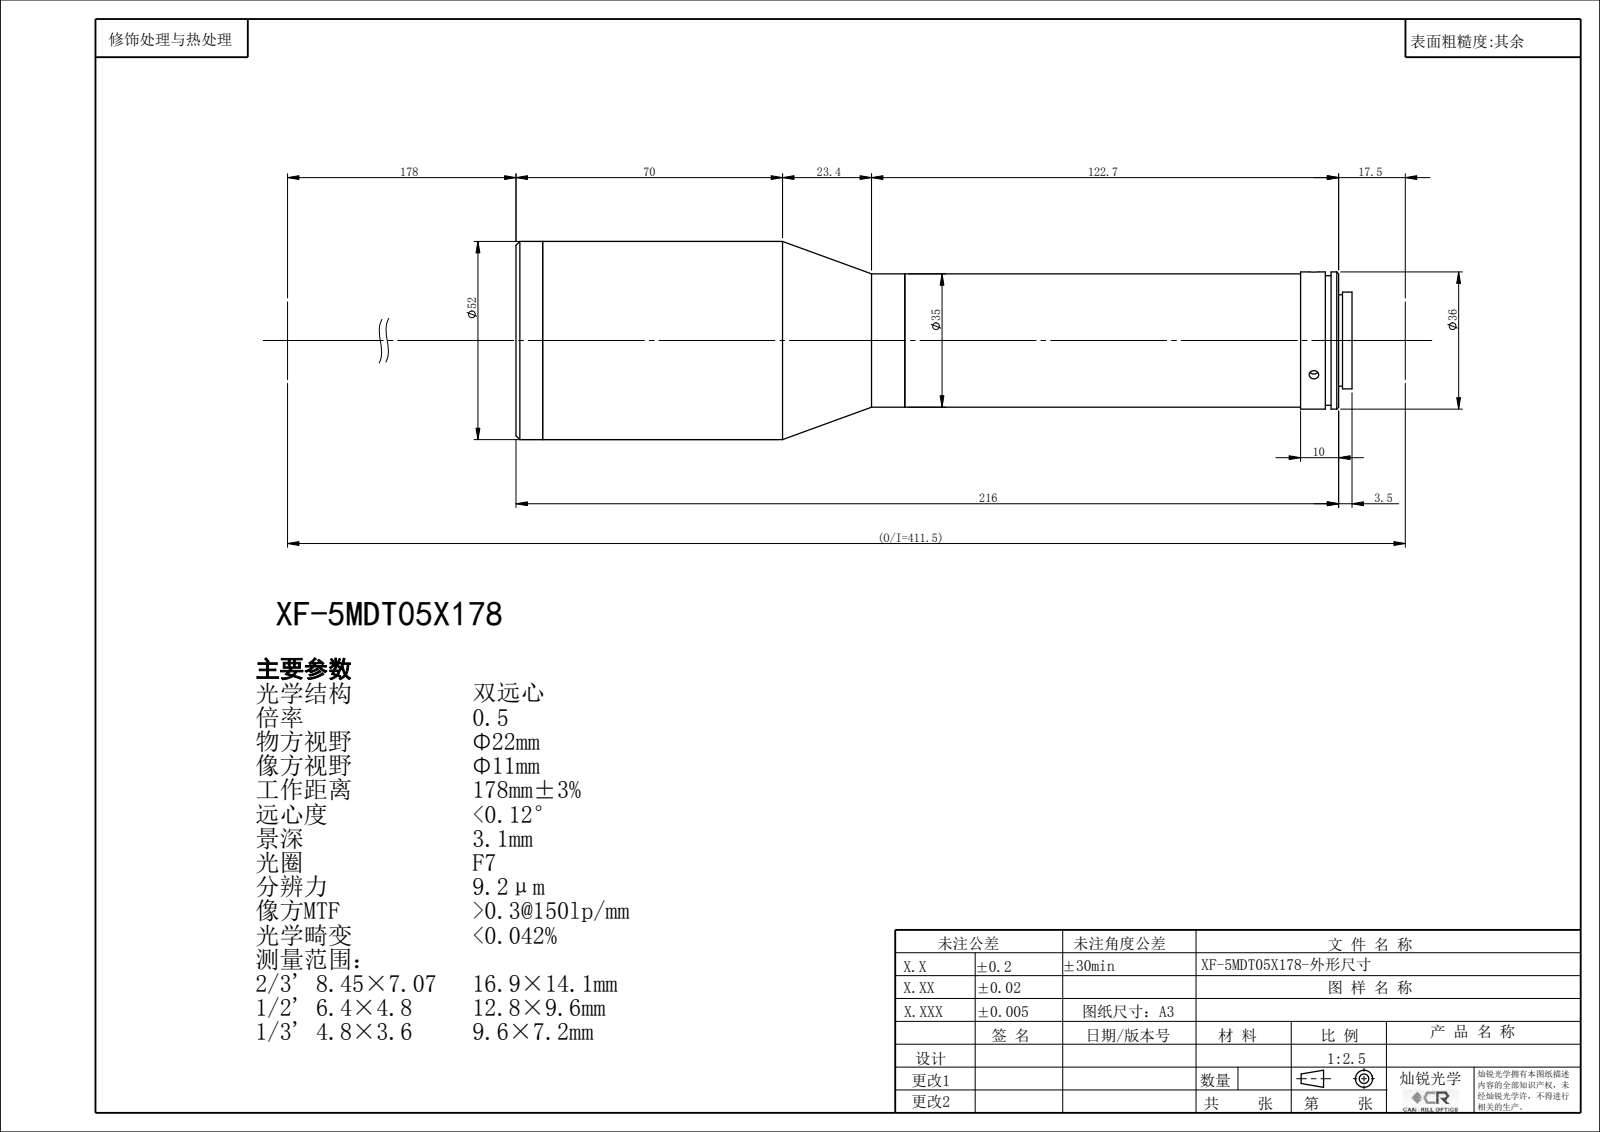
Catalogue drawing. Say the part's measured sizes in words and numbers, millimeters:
The part is named "XF-5MDT05X178". Its 3-D file was written by "SolidWorks 2014 (CONFIG_CONTROL_DESIGN)". It is 0 solids with 65 faces: 19 planar, 36 cylindrical and 10 other. Overall it measures 219.53 by 52 by 52 millimeters. Round holes: 3 of diameter 2.5, 1 of diameter 21.4, 1 of diameter 26, 1 of diameter 40, 1 of diameter 44.4, 1 of diameter 48. Round bosses or shafts: 1 of diameter 52, 1 of diameter 36, 1 of diameter 35, 1 of diameter 34, 1 of diameter 25.4, 1 of diameter 24. The main face-to-face distances are 113.93, 102.1, 216.03, 0.43, 101.67, 215.6, 7, 206.03, 205.6, 103.93.
